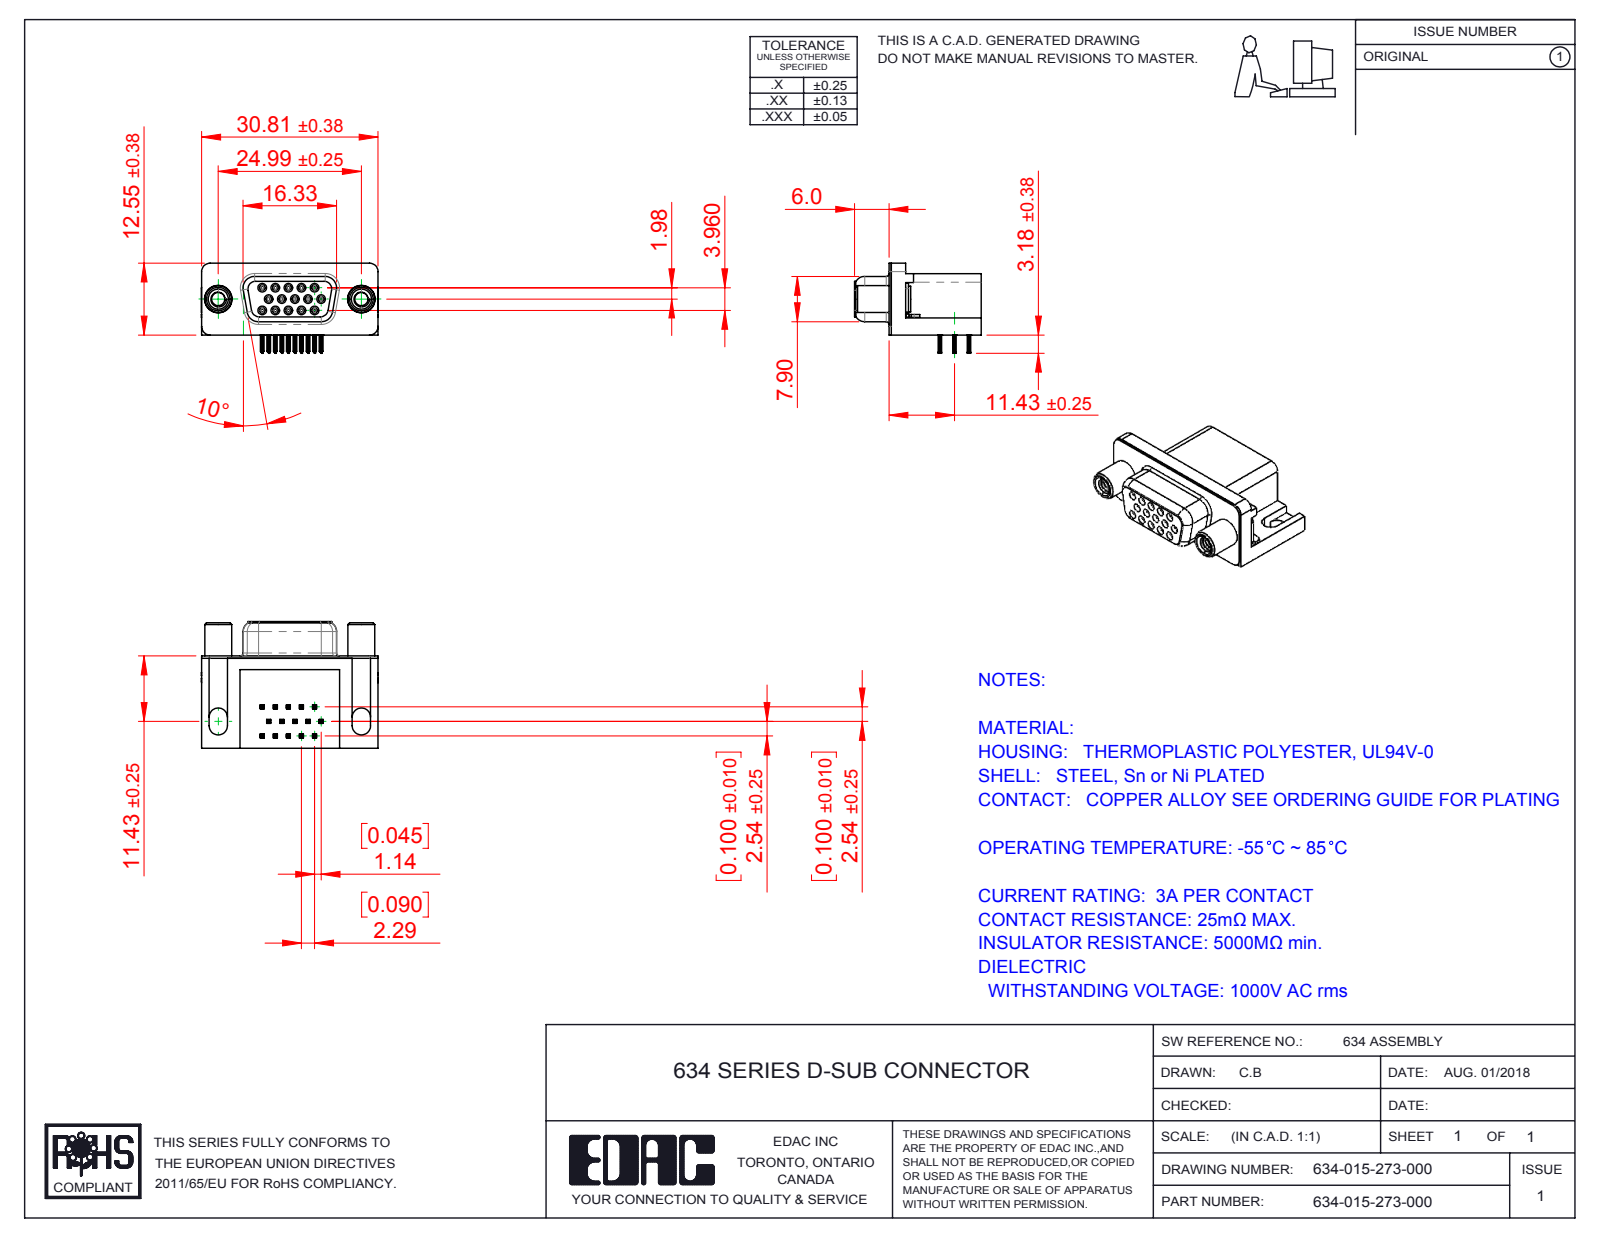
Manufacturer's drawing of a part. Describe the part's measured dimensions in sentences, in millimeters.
The part is named "Round Threaded Standoff; Contact Middle_Recessed; 634 Housing; Contact Middle (+5 more)". Its 3-D file was written by "SolidWorks 2016 (CONFIG_CONTROL_DESIGN)". It is 21 solids with 2411 faces: 1058 planar, 603 cylindrical and 750 other. Overall it measures 30.89 by 22.1 by 15.73 millimeters. Its volume is 4 596 cubic millimeters and its surface area 6 474 square millimeters. Round holes: 15 of diameter 0.8, 15 of diameter 0.9, 2 of diameter 2.3, 2 of diameter 3.1, 2 of diameter 4, 2 of diameter 4.8, 2 of diameter 5. Round bosses or shafts: 15 of diameter 1.2, 2 of diameter 4.9, 2 of diameter 4.7, 2 of diameter 4.5, 2 of diameter 3.85. Partial cylindrical surfaces (rounded edges, fillets, slot ends): 120 of radius 0.1, 60 of radius 0.15, 30 of radius 0.35, 19 of radius 1, 15 of radius 0.34, 8 of radius 1.35, 8 of radius 1.6, 7 of radius 1.5. The main face-to-face distances are 0.4, 10.35, 15.7, 16.1, 2.5, 6.7, 2.9, 0.35, 10.7, 13.2. The hole center spacings are 2.29, 2.28, 3.96, 4.57, 6.05, 3.97, 4.58, 6.86.
